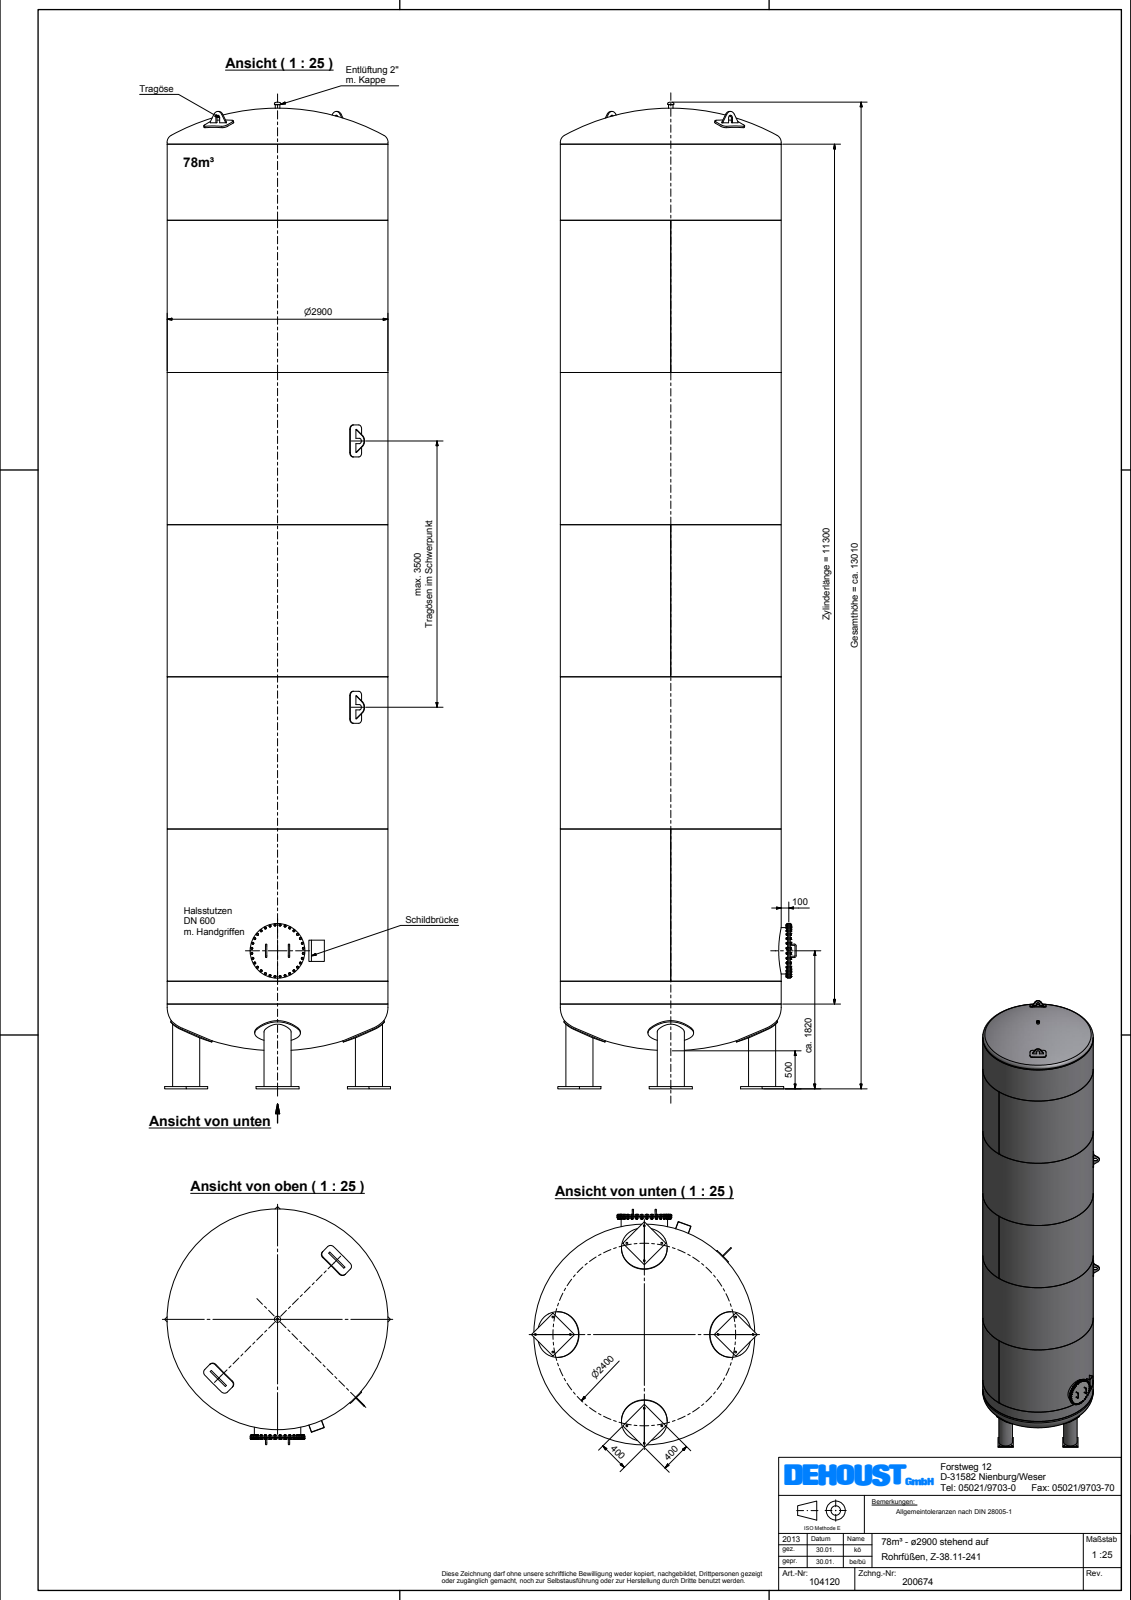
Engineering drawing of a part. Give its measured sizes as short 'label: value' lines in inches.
name: Beh\S\dlter_Z-38_11-241_2900_078_KV
written by: Autodesk Inventor 2012 (AUTOMOTIVE_DESIGN)
unit: in
bodies: 5 solids, 1148 faces (648 planar, 172 cylindrical, 328 other)
size: 510.512 × 123.222 × 116.759
volume: 215 200 in³; area: 382 400 in²
holes: 4× ⌀9.055, 4× ⌀13.252, 1× ⌀23.543, 1× ⌀113.386, 1× ⌀113.622, 1× ⌀113.701
bosses: 38× ⌀0.63, 32× ⌀0.886, 4× ⌀23.622, 4× ⌀14, 1× ⌀114.173, 1× ⌀28.346, 1× ⌀25.984, 1× ⌀24.016
rounds: 16× R2.205, 4× R1.378, 4× R3.346, 1× R57.48
face distances: 43.86, 1.181, 42.679, 1.378, 0.63, 0.748, 0.119, 15.746, 66.803, 0.394
hole spacings: 47.244, 66.813, 94.488
